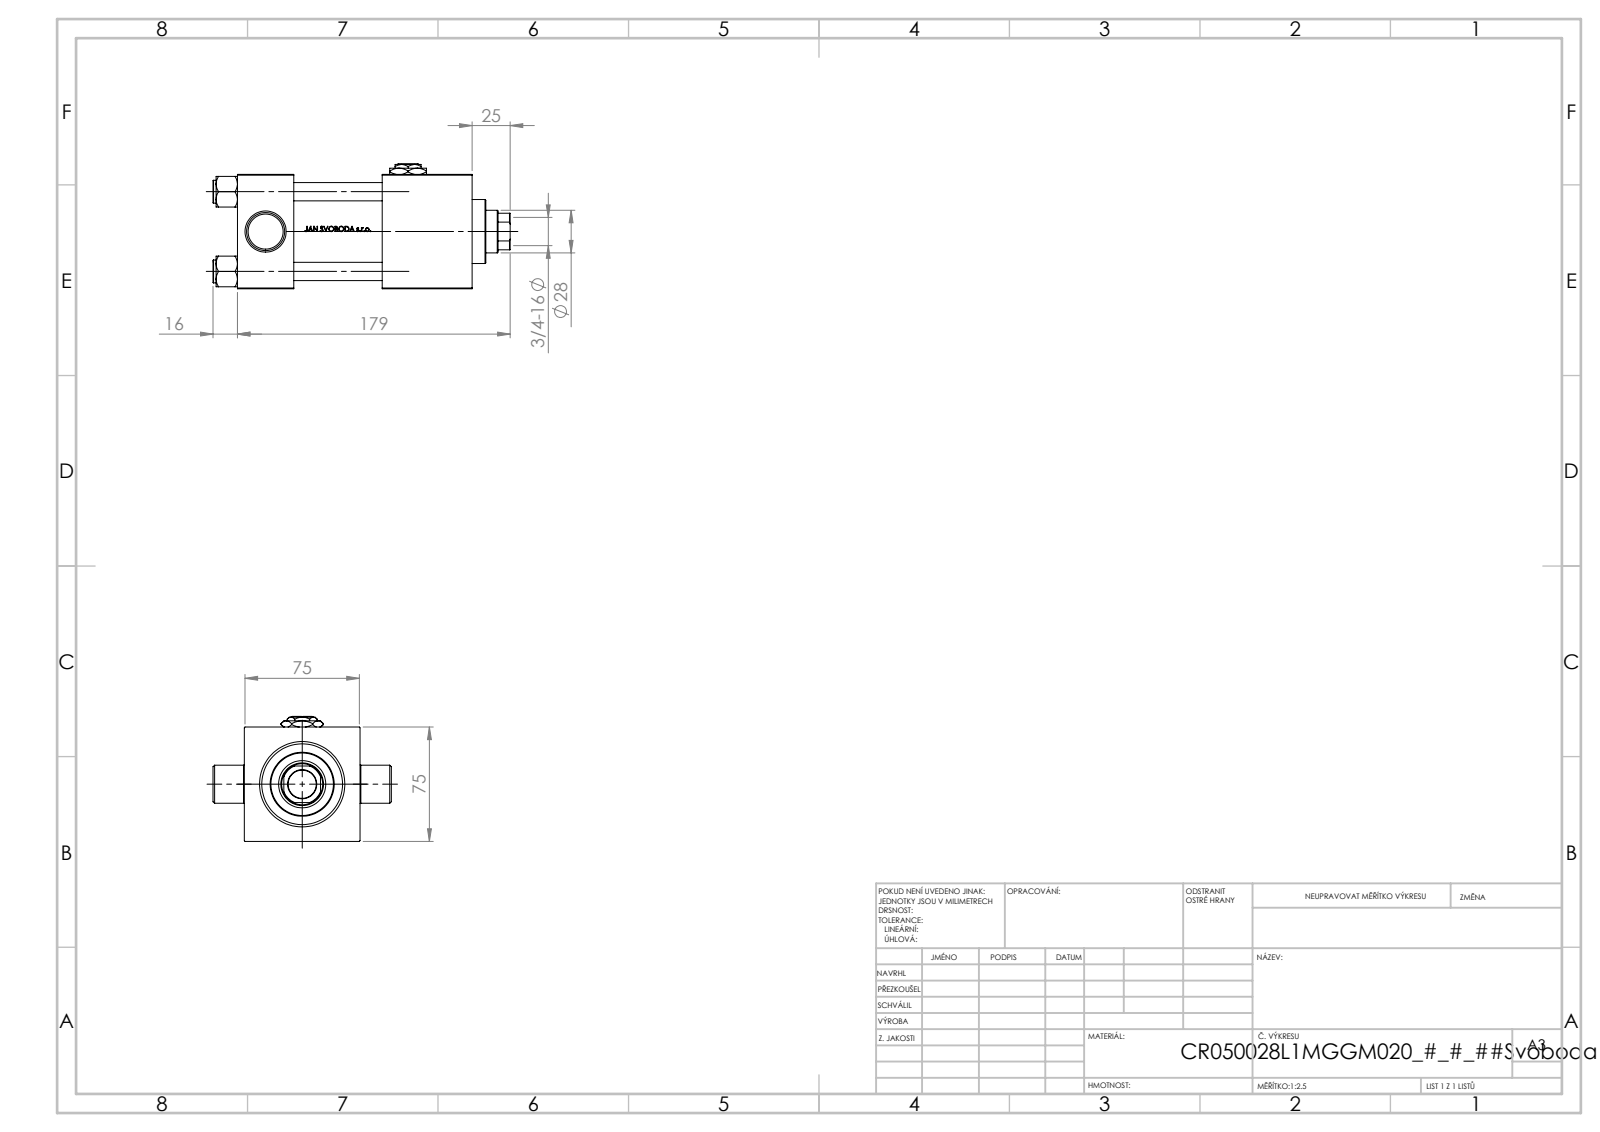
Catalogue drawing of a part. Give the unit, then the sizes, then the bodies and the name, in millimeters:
Units: millimetres
Overall size (bounding box): 195 × 117 × 82
Round holes (diameter × count): ⌀12 ×4, ⌀7 ×2, ⌀20.96 ×2, ⌀30 ×2, ⌀18.5 ×1, ⌀28 ×1, ⌀31 ×1, ⌀41 ×1, ⌀50 ×1, ⌀53 ×1
Round bosses / shafts (diameter × count): ⌀15 ×4, ⌀56 ×1, ⌀42 ×1, ⌀25 ×1
Partial cylindrical surfaces — rounded edges, fillets, slot ends (radius × count): R13.5 ×1
Main face-to-face distances: 75, 37, 0.5, 117, 76, 75.5, 154, 59, 58, 95
Hole centre spacings: 36.98, 52.3, 73.96, 93.5
Volume: 698 969 mm³ · Surface area: 151 186 mm²
Bodies: 12 solids, 1119 faces (451 planar, 124 cylindrical, 544 other)
Part name (STEP PRODUCT): NUT_M5_L; Zatka_pro_OIL_PORT; V215CR_L_Body; V215CR_VCP_L (+2 more)
STEP written by: SolidWorks 2019 (CONFIG_CONTROL_DESIGN)
